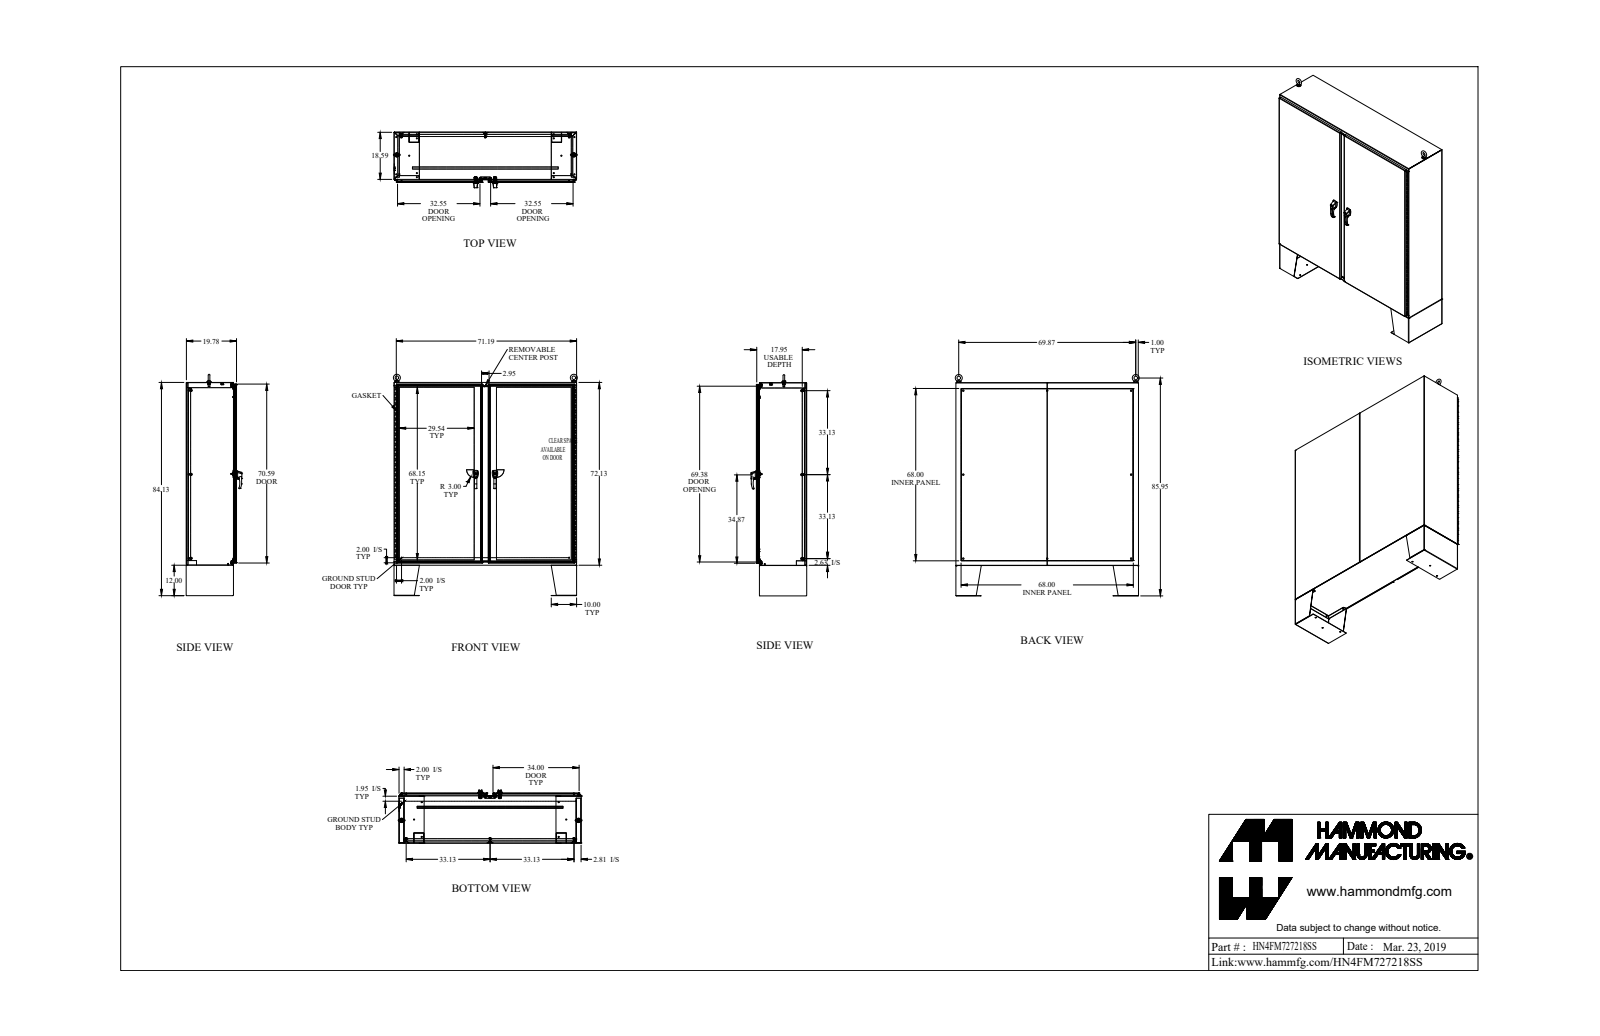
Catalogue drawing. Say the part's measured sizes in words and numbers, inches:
The part is named "HN4FM727218SS". Its 3-D file was written by "SolidWorks 2018 (AUTOMOTIVE_DESIGN)". It is 131 solids with 3990 faces: 1826 planar, 1803 cylindrical and 361 other. Overall it measures 87.321 by 72.607 by 21.99 inches. Its volume is 2 556 cubic inches and its surface area 51 127 square inches. Round holes: 24 of diameter 0.304, 14 of diameter 0.437, 8 of diameter 0.307, 8 of diameter 0.35, 8 of diameter 0.563, 6 of diameter 0.25, 6 of diameter 0.445, 4 of diameter 0.281, 4 of diameter 0.313, 4 of diameter 0.39, 3 of diameter 0.201, 3 of diameter 0.313. Round bosses or shafts: 10 of diameter 1, 8 of diameter 0.65, 8 of diameter 0.375, 8 of diameter 0.332, 4 of diameter 0.75, 4 of diameter 0.625, 4 of diameter 0.44, 4 of diameter 0.37. Partial cylindrical surfaces (rounded edges, fillets, slot ends): 33 of radius 0.5, 32 of radius 0.018, 32 of radius 0.125, 29 of radius 0.048, 29 of radius 0.143, 28 of radius 0.06, 12 of radius 0.03, 12 of radius 0.09. The main face-to-face distances are 0.095, 19.78, 19.685, 0.125, 17.998, 19.875, 1.782, 1.687, 18.093, 1.657. The hole center spacings are 6, 12, 18, 24, 74.07, 30, 36, 66.25.
